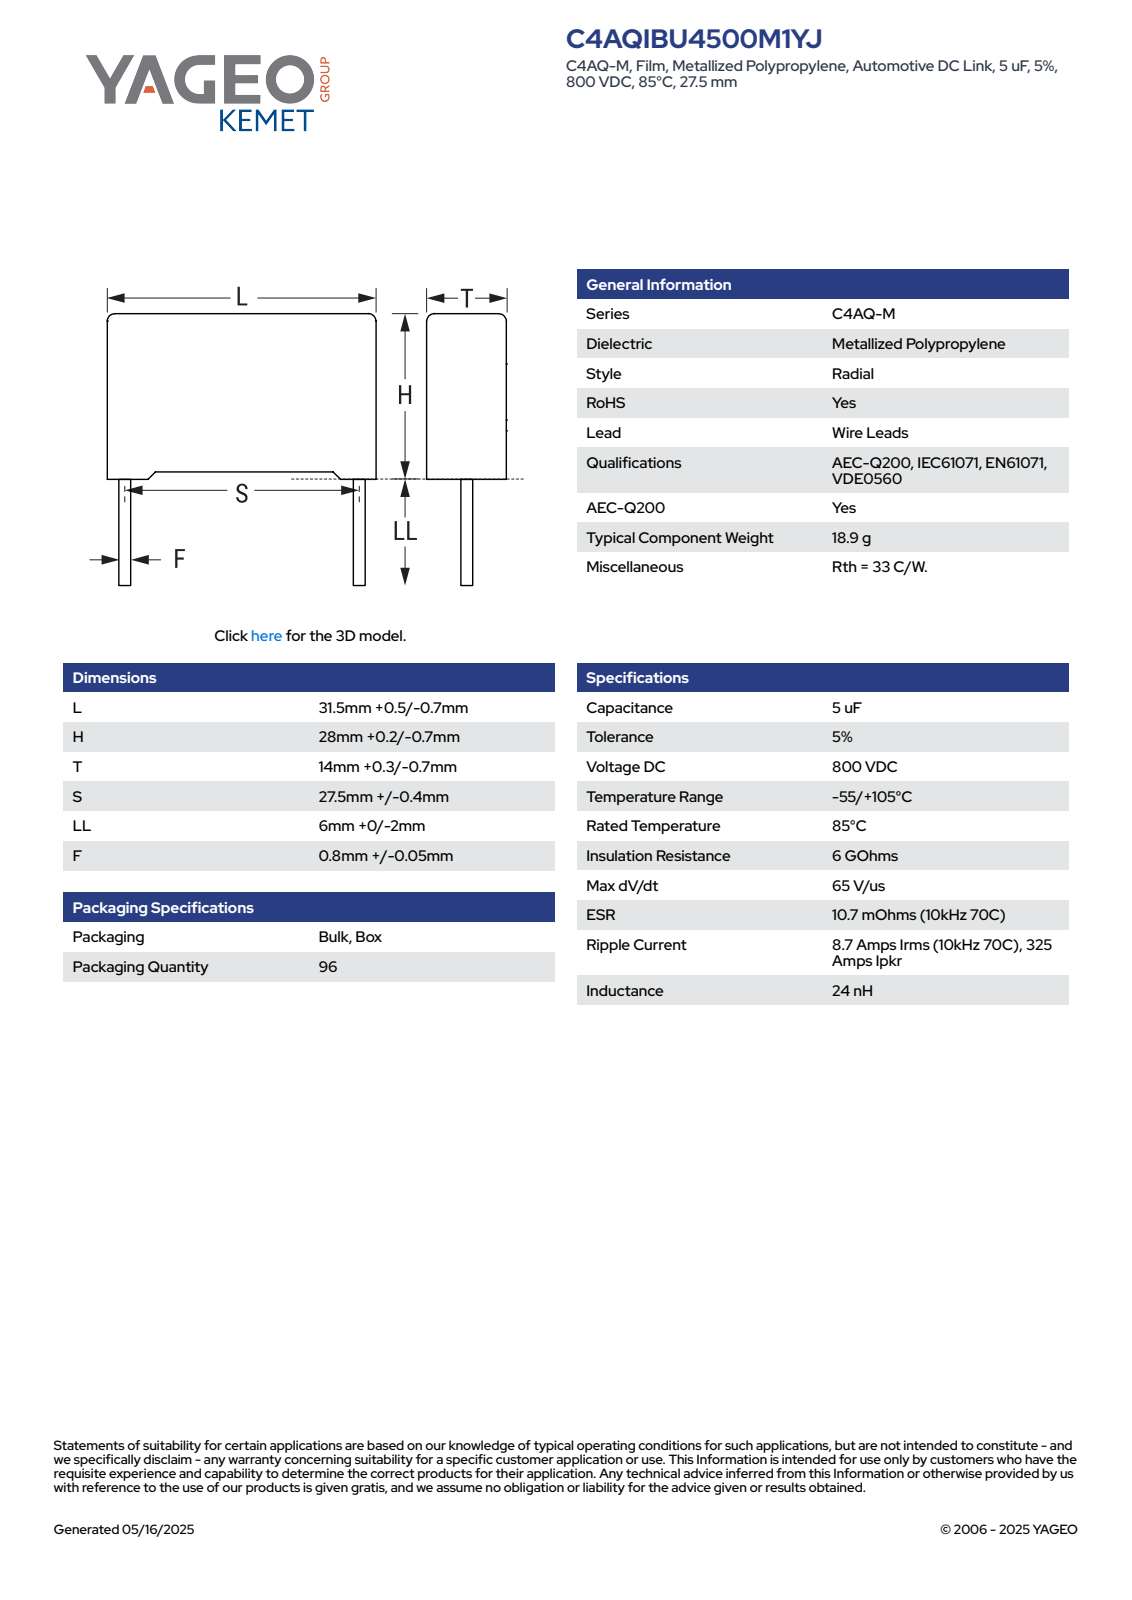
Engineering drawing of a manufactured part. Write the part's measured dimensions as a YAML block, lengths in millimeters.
part_name: "CFR_RB2CFP_31.5X28X14_L32H28.2T14.3S27.5LL6F0.85"
step_written_by: "SolidWorks 2014 (AUTOMOTIVE_DESIGN)"
units: millimeters
bodies: {solids: 4, faces: 85, planar: 77, cylindrical: 8, other: 0}
overall_size: [34.2, 32, 14.3]
volume: 12524
surface_area: 3605
round_bosses_or_shafts:
  - {diameter: 0.85, count: 2}
partial_cylinders:
  - {radius: 0.5, count: 4}
face_to_face_distances: [14.3, 32, 27.23, 27.45, 0.75, 0.97, 28.2, 1.07, 30.93, 29.86]
